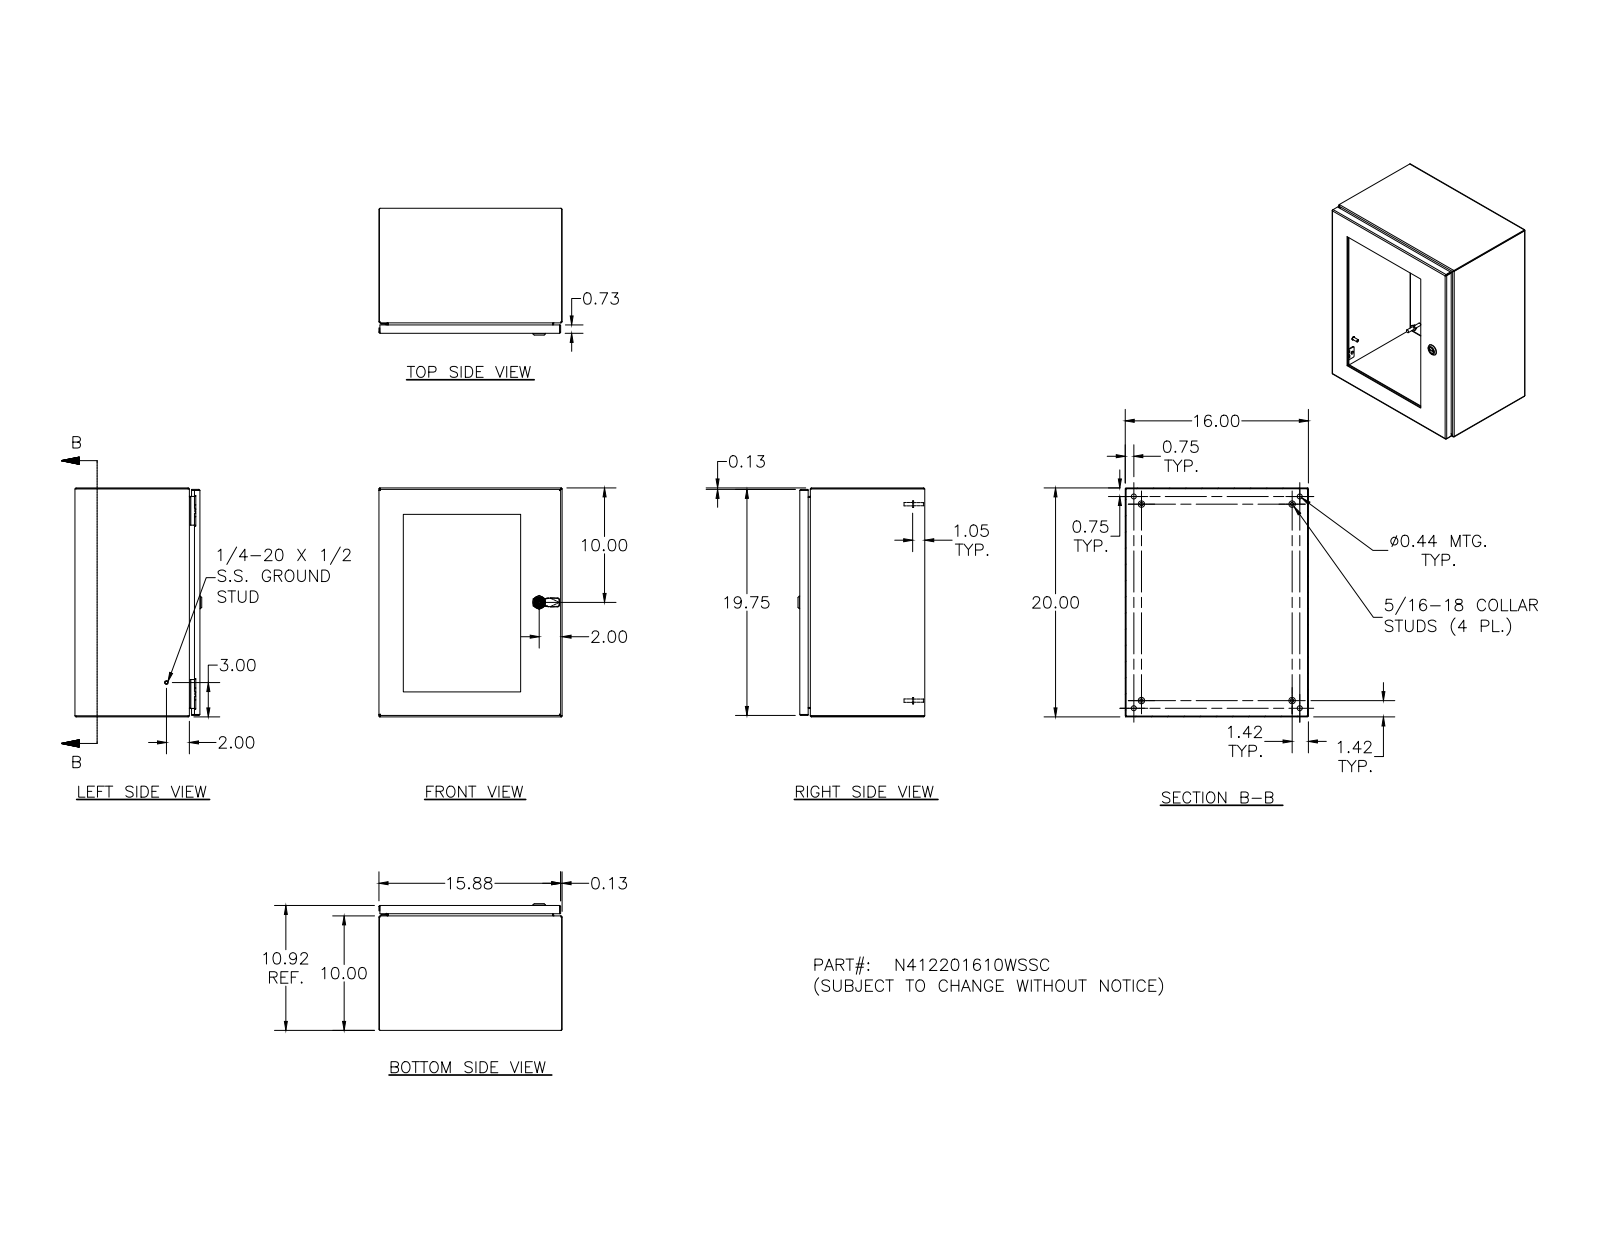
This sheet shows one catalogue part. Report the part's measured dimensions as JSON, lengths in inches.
{"part_name": "N412201610WSSC; N412201610WSSCBKP; N4122016WSSCLID; HFW328176 (+8 more)", "step_written_by": "Autodesk Inventor 2011 (AUTOMOTIVE_DESIGN)", "units": "inches", "bodies": {"solids": 66, "faces": 1876, "planar": 732, "cylindrical": 557, "other": 587}, "overall_size": [20, 16, 11.075], "volume_in3": 150.9, "surface_area_in2": 3244, "round_holes": [[0.156, 16], [0.281, 14], [0.093, 4], [0.152, 4], [0.167, 4], [0.172, 4], [0.188, 4], [0.437, 4], [0.187, 1], [0.197, 1], [0.315, 1], [0.394, 1]], "round_bosses_or_shafts": [[0.19, 14], [0.253, 13], [0.25, 10], [0.563, 4], [0.36, 4], [0.32, 4], [0.3, 4], [0.275, 4]], "partial_cylinders_radius": [[0.031, 34], [0.05, 26], [0.105, 24], [0.016, 18], [0.125, 16], [0.02, 9], [0.032, 8], [0.157, 4]], "face_to_face_distances": [0.074, 10.843, 15.926, 10.769, 19.926, 16, 15.852, 0.25, 10.593, 10.519], "hole_center_spacings": [4, 8, 12.176, 16, 6.221, 8.585, 10.035, 11.5]}
